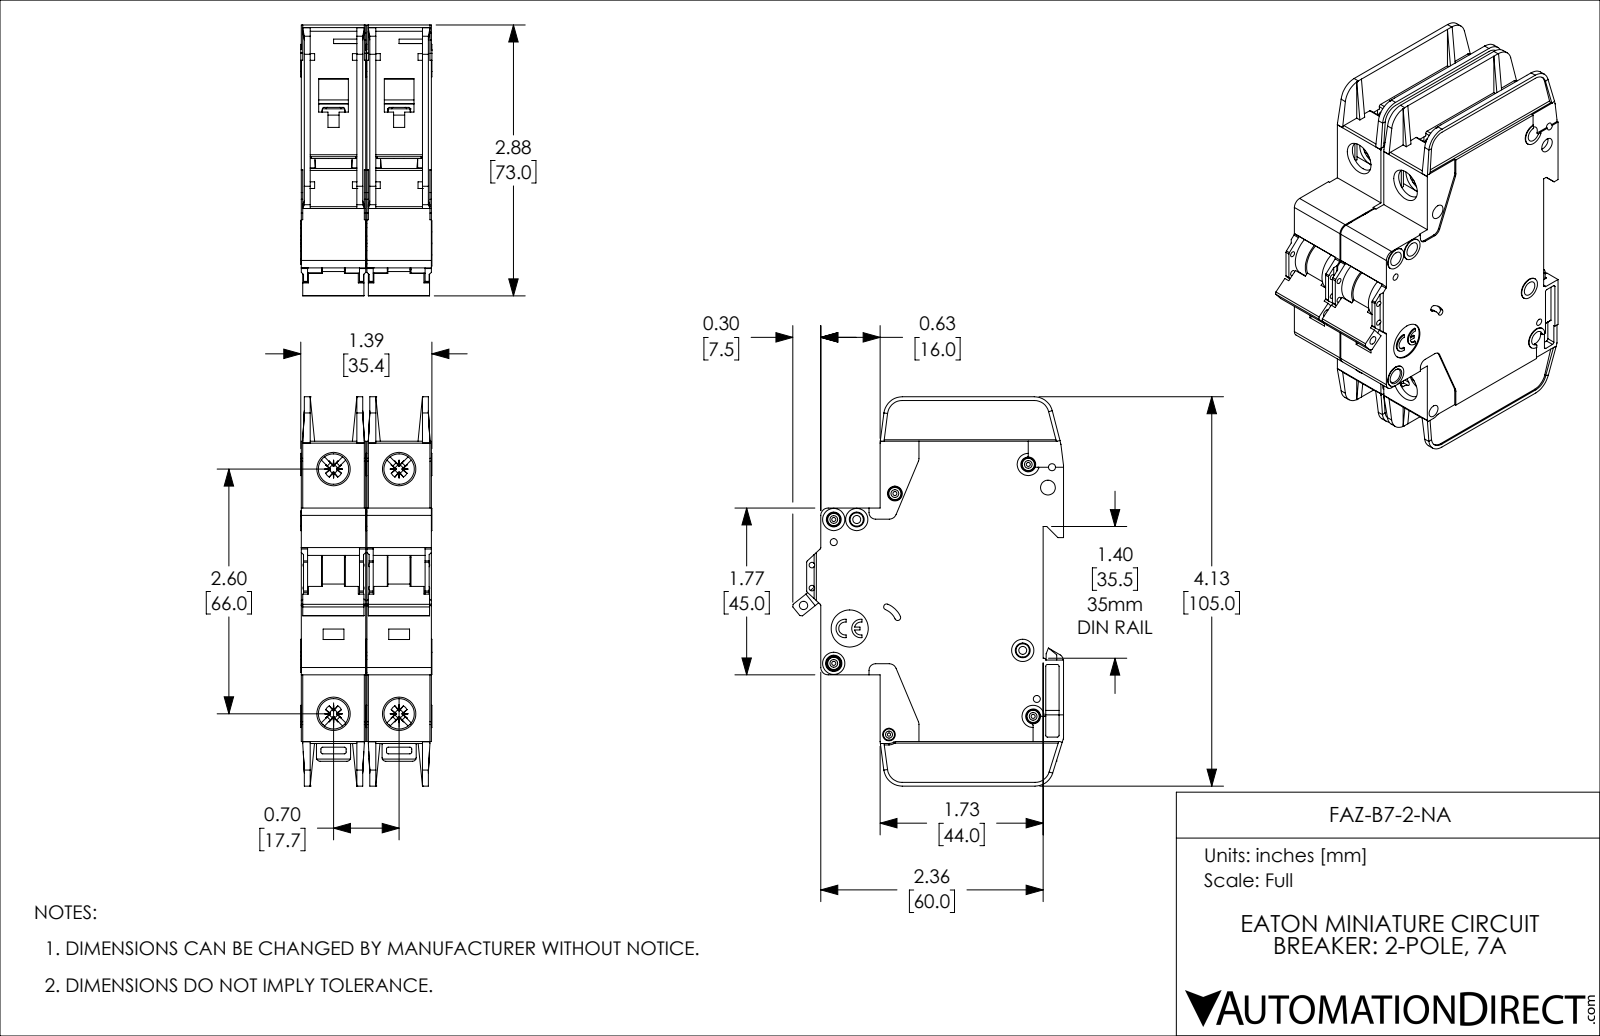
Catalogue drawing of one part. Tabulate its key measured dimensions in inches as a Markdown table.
| quantity | value |
| --- | --- |
| part name | FAZ-B7-2-NA |
| STEP written by | SolidWorks 2019 (AUTOMOTIVE_DESIGN) |
| units | inches |
| bodies | 2 solids, 2254 faces (1342 planar, 714 cylindrical, 198 other) |
| overall size | 4.134 × 2.876 × 1.394 |
| volume | 9.365 in³ |
| surface area | 82.01 in² |
| round holes (diameter × count) | 0.157 × 8, 0.043 × 5, 0.075 × 4, 0.323 × 4, 0.059 × 2, 0.085 × 2, 0.035 × 1, 0.089 × 1, 0.098 × 1, 0.134 × 1, 0.394 × 1 |
| round bosses / shafts (diameter × count) | 0.13 × 5, 0.236 × 4, 0.118 × 3, 0.098 × 2 |
| partial cylindrical surfaces (radius × count) | 0.02 × 57, 0.016 × 20, 0.039 × 14, 0.079 × 10, 0.043 × 8, 0.008 × 5, 0.197 × 5, 0.01 × 4 |
| main face-to-face distances | 0.697, 0.047, 0.685, 0.591, 0.094, 0.638, 0.543, 1.382, 0.744, 0.65 |
| hole center spacings | 0.244, 0.537, 0.697, 0.87, 2.598, 2.69, 0.189, 0.199 |
